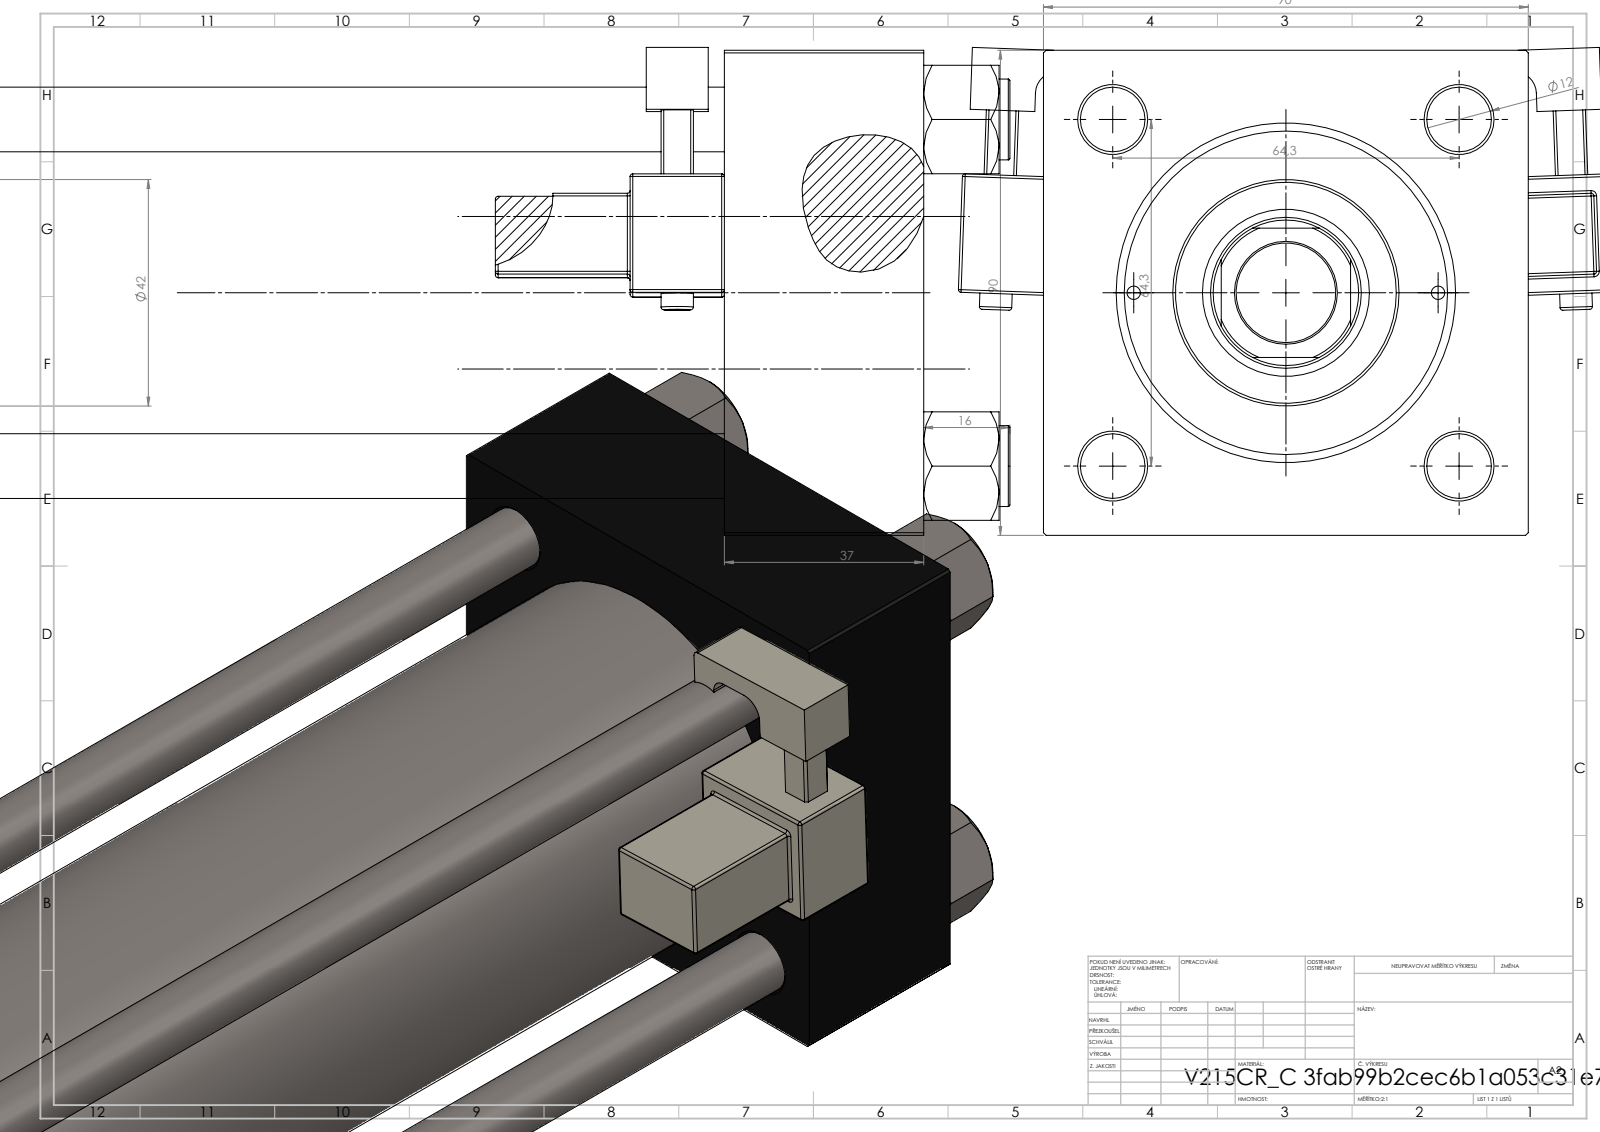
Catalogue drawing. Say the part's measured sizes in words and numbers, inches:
The part is named "V215CR_VCP_C; NUT_M5_C; V215CR_MSU; V215CR_C_TYCINKA (+2 more)". Its 3-D file was written by "SolidWorks 2019 (CONFIG_CONTROL_DESIGN)". It is 13 solids with 1308 faces: 586 planar, 150 cylindrical and 572 other. Overall it measures 15.079 by 4.786 by 3.564 inches. Its volume is 78.84 cubic inches and its surface area 479.1 square inches. Round holes: 4 of diameter 0.472, 2 of diameter 0.098, 2 of diameter 0.276, 2 of diameter 0.825, 2 of diameter 1.181, 1 of diameter 0.728, 1 of diameter 1.102, 1 of diameter 1.22, 1 of diameter 1.969, 1 of diameter 2.362, 1 of diameter 2.48. Round bosses or shafts: 4 of diameter 0.591, 2 of diameter 0.236, 1 of diameter 2.717, 1 of diameter 1.654. Partial cylindrical surfaces (rounded edges, fillets, slot ends): 48 of radius 0.02, 2 of radius 0.039, 2 of radius 0.098, 2 of radius 0.157, 1 of radius 0.531. The main face-to-face distances are 3.543, 1.457, 13.189, 11.732, 10.866, 9.409, 2.323, 12.059, 10.602, 1.193. The hole center spacings are 1.275, 1.79, 2.531, 2.694, 1.112, 3.58, 2.224, 10.925.
